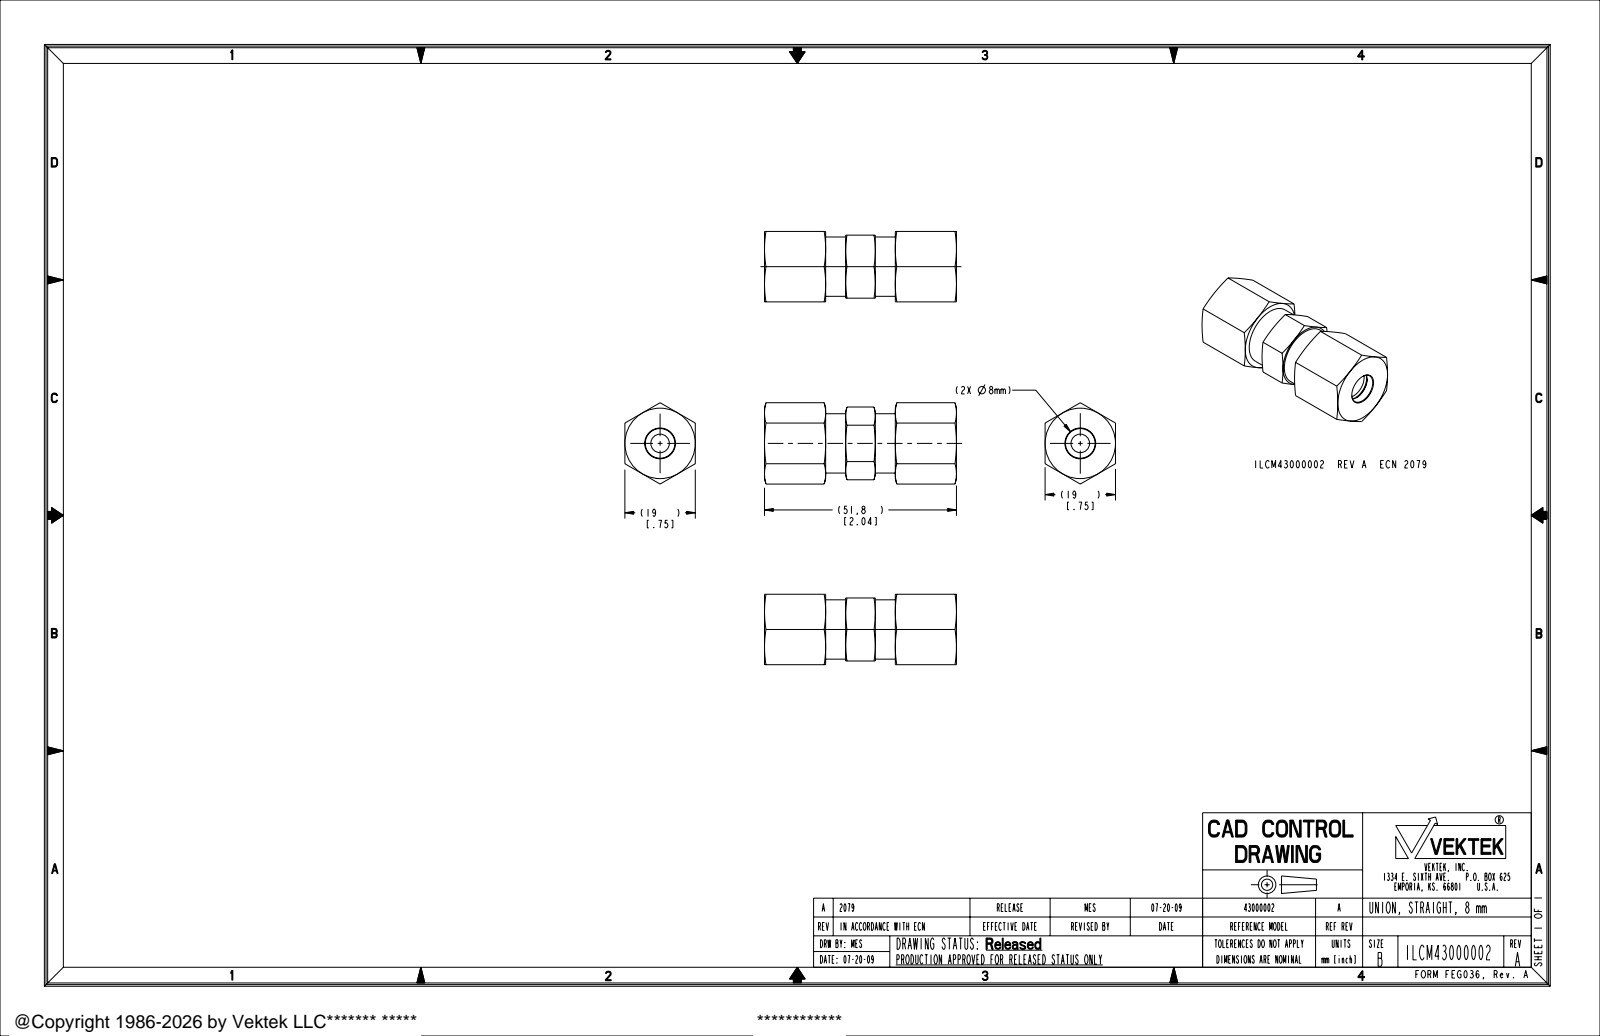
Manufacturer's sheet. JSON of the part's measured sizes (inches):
{"part_name": "ILCM43000002", "step_written_by": "PRO/ENGINEER BY PARAMETRIC TECHNOLOGY CORPORATION, 2007460 (AUTOMOTIVE_DESIGN_CC2)", "units": "inches", "bodies": {"solids": 1, "faces": 132, "planar": 34, "cylindrical": 30, "other": 68}, "overall_size": [2.039, 0.864, 0.748], "volume_in3": 0.706, "surface_area_in2": 9.999, "round_holes": [[0.197, 1], [0.315, 1], [0.566, 1]], "round_bosses_or_shafts": [[0.63, 1], [0.433, 1], [0.398, 1]], "face_to_face_distances": [0.748, 0.709, 0.039, 2.039, 0.669, 0.65, 1.39, 0.39, 1.65, 0.26]}
